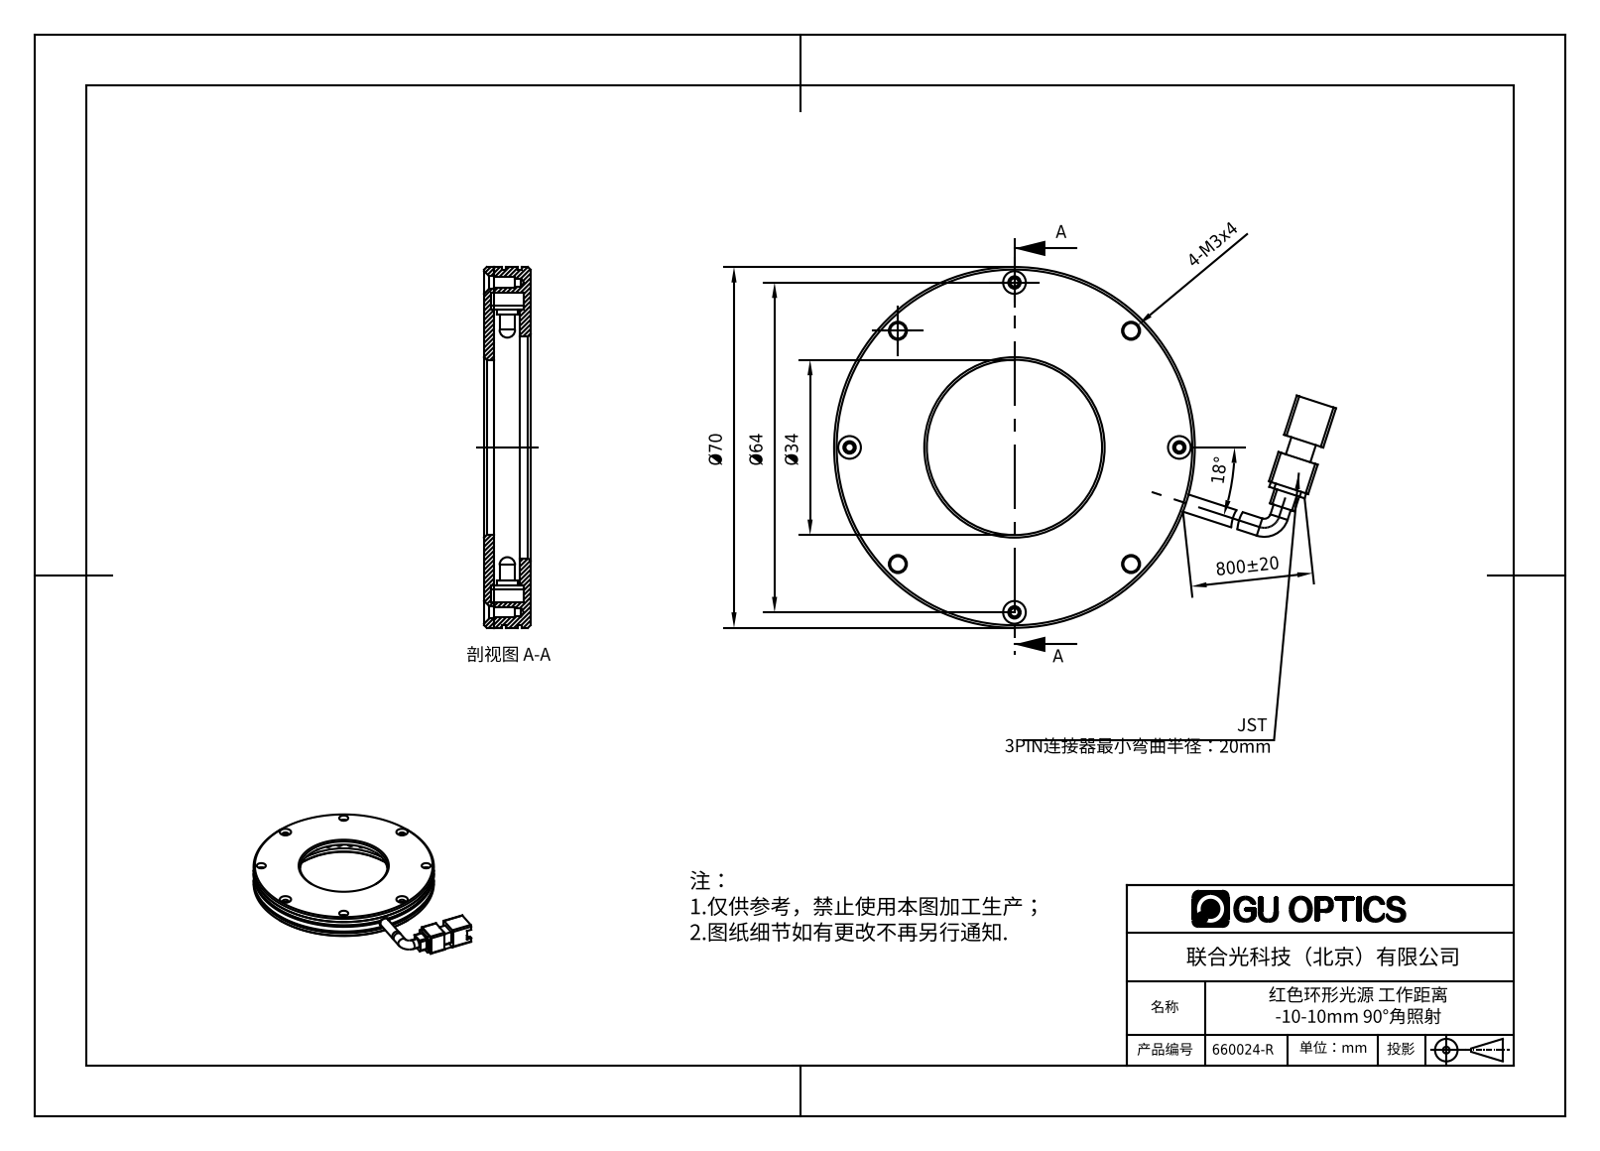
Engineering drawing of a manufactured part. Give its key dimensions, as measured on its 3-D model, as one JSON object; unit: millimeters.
{"part_name": "660024-R", "step_written_by": "SolidWorks 2016 (AUTOMOTIVE_DESIGN)", "units": "millimeters", "bodies": {"solids": 37, "faces": 771, "planar": 464, "cylindrical": 242, "other": 65}, "overall_size": [97.4, 70, 11], "volume_mm3": 17278, "surface_area_mm2": 21297, "round_holes": [[1.6, 4], [2, 4], [2.4, 4], [3, 4], [3.5, 4], [3.6, 1], [3.8, 1], [34, 1], [43, 1], [54, 1], [60, 1]], "round_bosses_or_shafts": [[3, 32], [3.8, 31], [3.5, 2], [70, 1], [69, 1], [54.8, 1], [53.6, 1]], "partial_cylinders_radius": [[0.5, 8], [1, 4], [1.5, 2], [33, 1]], "face_to_face_distances": [2, 7, 9, 0.6, 7.6, 5.6, 1.4, 5, 6.2, 1], "hole_center_spacings": [24.49, 32, 59.13, 45.25, 45.26, 64, 64.01]}
